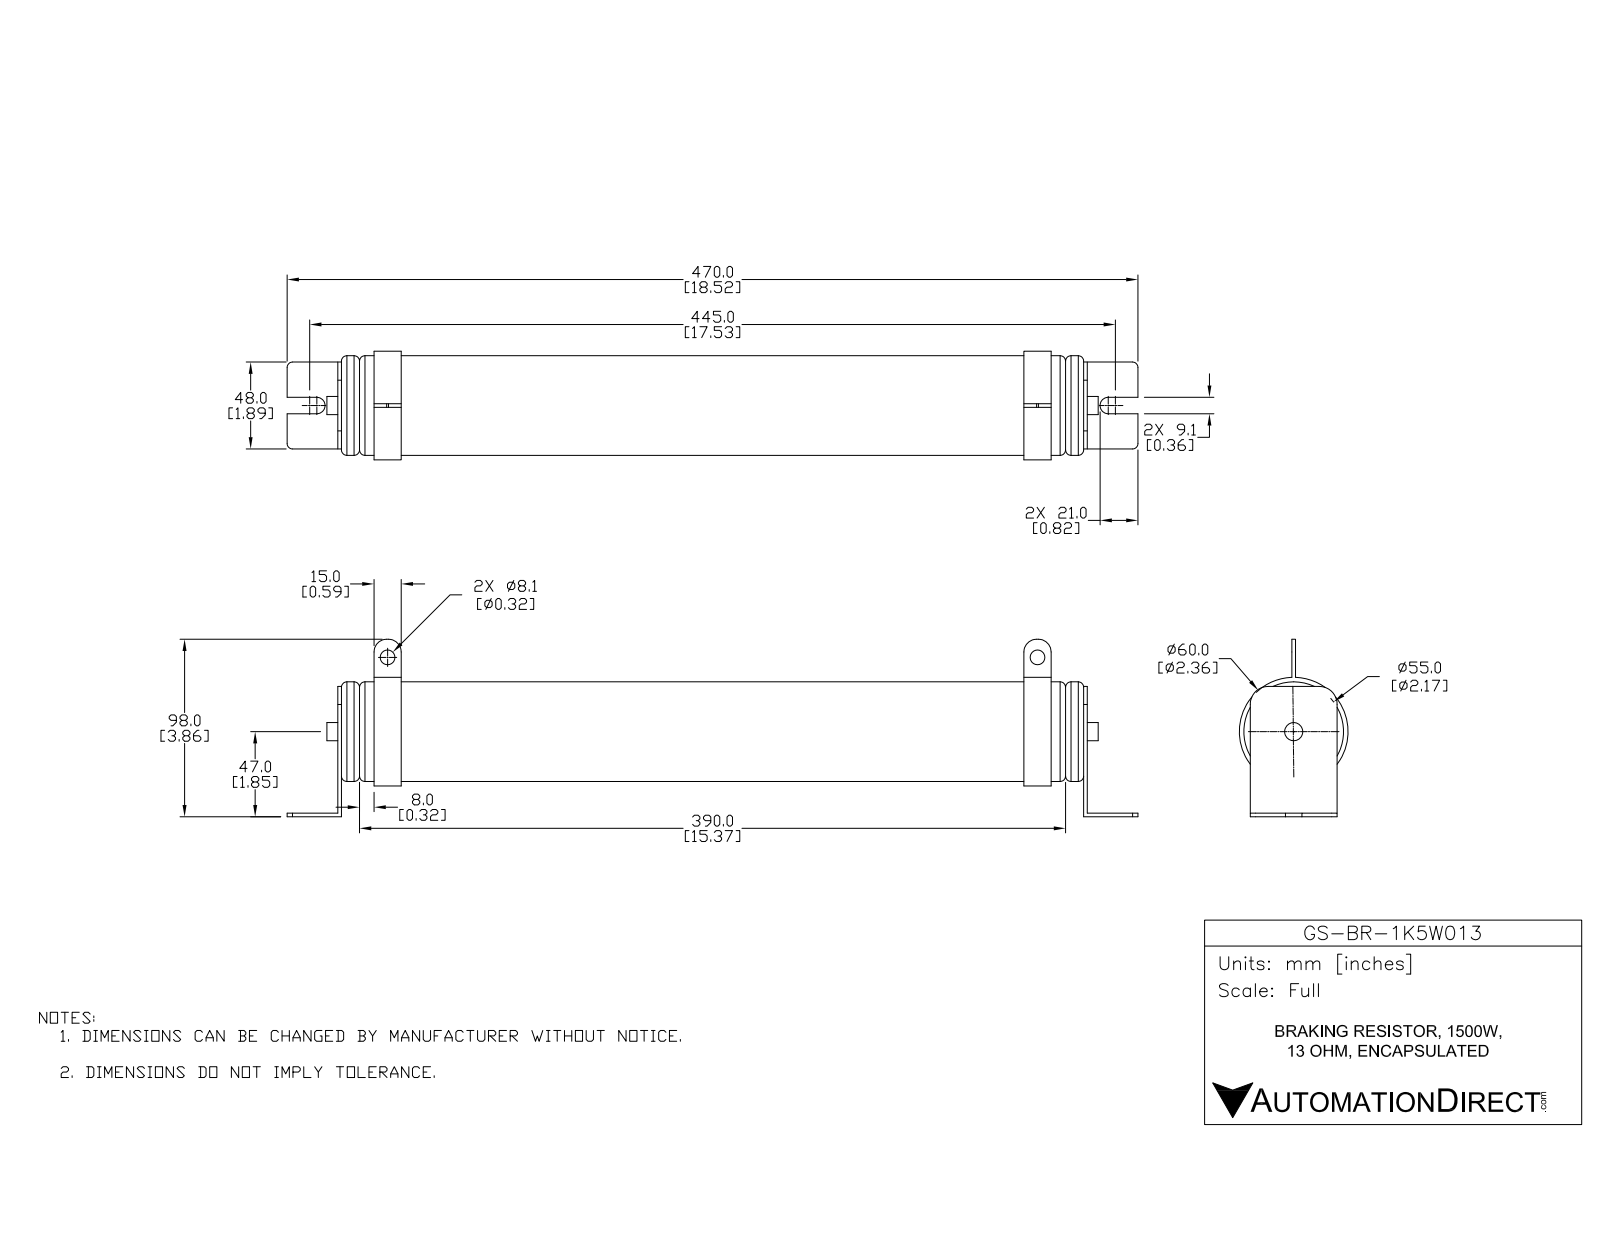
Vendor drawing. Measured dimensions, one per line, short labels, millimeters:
name: GS-BR-1K5W013
written by: SolidWorks 2015 (AUTOMOTIVE_DESIGN)
unit: mm
bodies: 2 solids, 91 faces (41 planar, 38 cylindrical, 12 other)
size: 470 × 98 × 60
volume: 1 006 000 mm³; area: 92 390 mm²
holes: 2× ⌀8.1
bosses: 1× ⌀60, 1× ⌀55, 1× ⌀55, 1× ⌀10
rounds: 4× R3, 4× R7, 2× R4.5, 2× R10
face distances: 2, 414, 412, 410, 35, 379, 33, 377, 20, 394
hole spacings: 359
